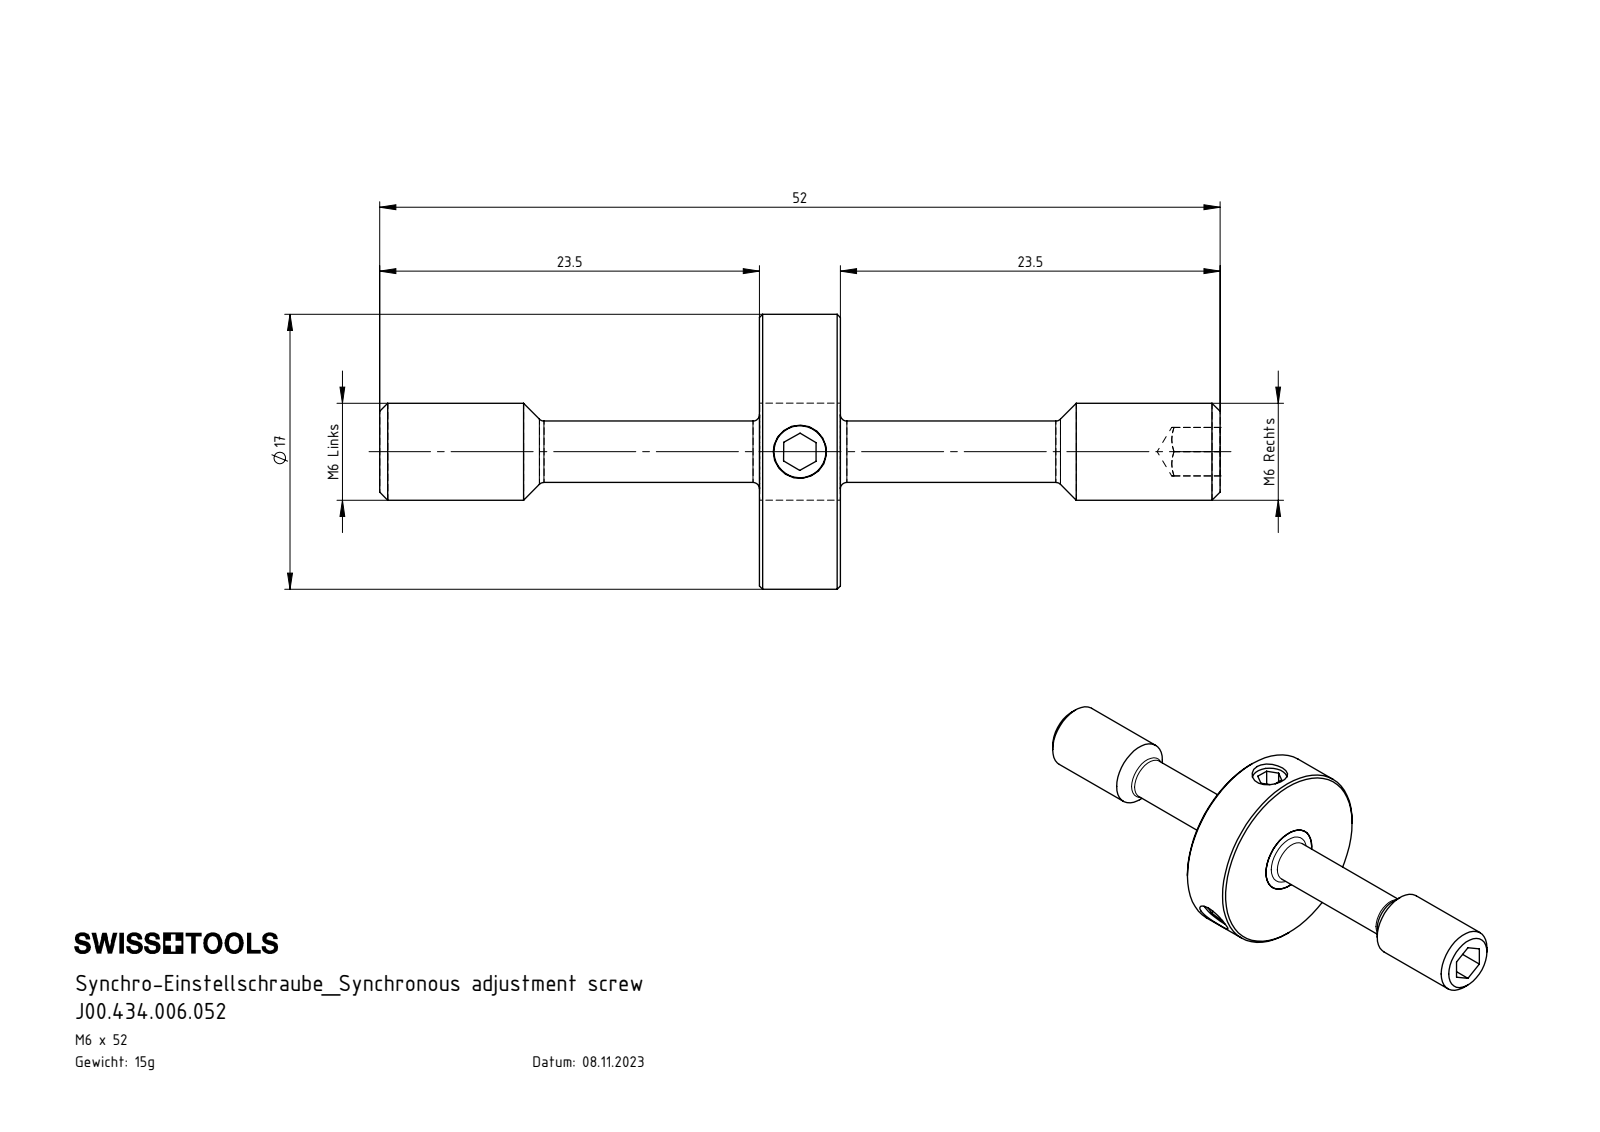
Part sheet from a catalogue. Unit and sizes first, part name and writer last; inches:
Units: inches
Overall size (bounding box): 2.047 × 0.669 × 0.669
Round holes (diameter × count): ⌀0.13 ×3
Round bosses / shafts (diameter × count): ⌀0.157 ×3, ⌀0.669 ×1, ⌀0.236 ×1, ⌀0.15 ×1
Main face-to-face distances: 0.197, 0.925, 1.122, 0.079, 0.098, 0.118, 2.047, 0.984, 1.063, 0.059
Volume: 0.12 in³ · Surface area: 3.204 in²
Bodies: 5 solids, 99 faces (39 planar, 26 cylindrical, 34 other)
Part name (STEP PRODUCT): Z42-ER3.002.005_A; Z55-ER3.001.052_A; ISO 4026 - M4 x 5; J00.434.006.052
STEP written by: SolidWorks 2022 (AUTOMOTIVE_DESIGN)
